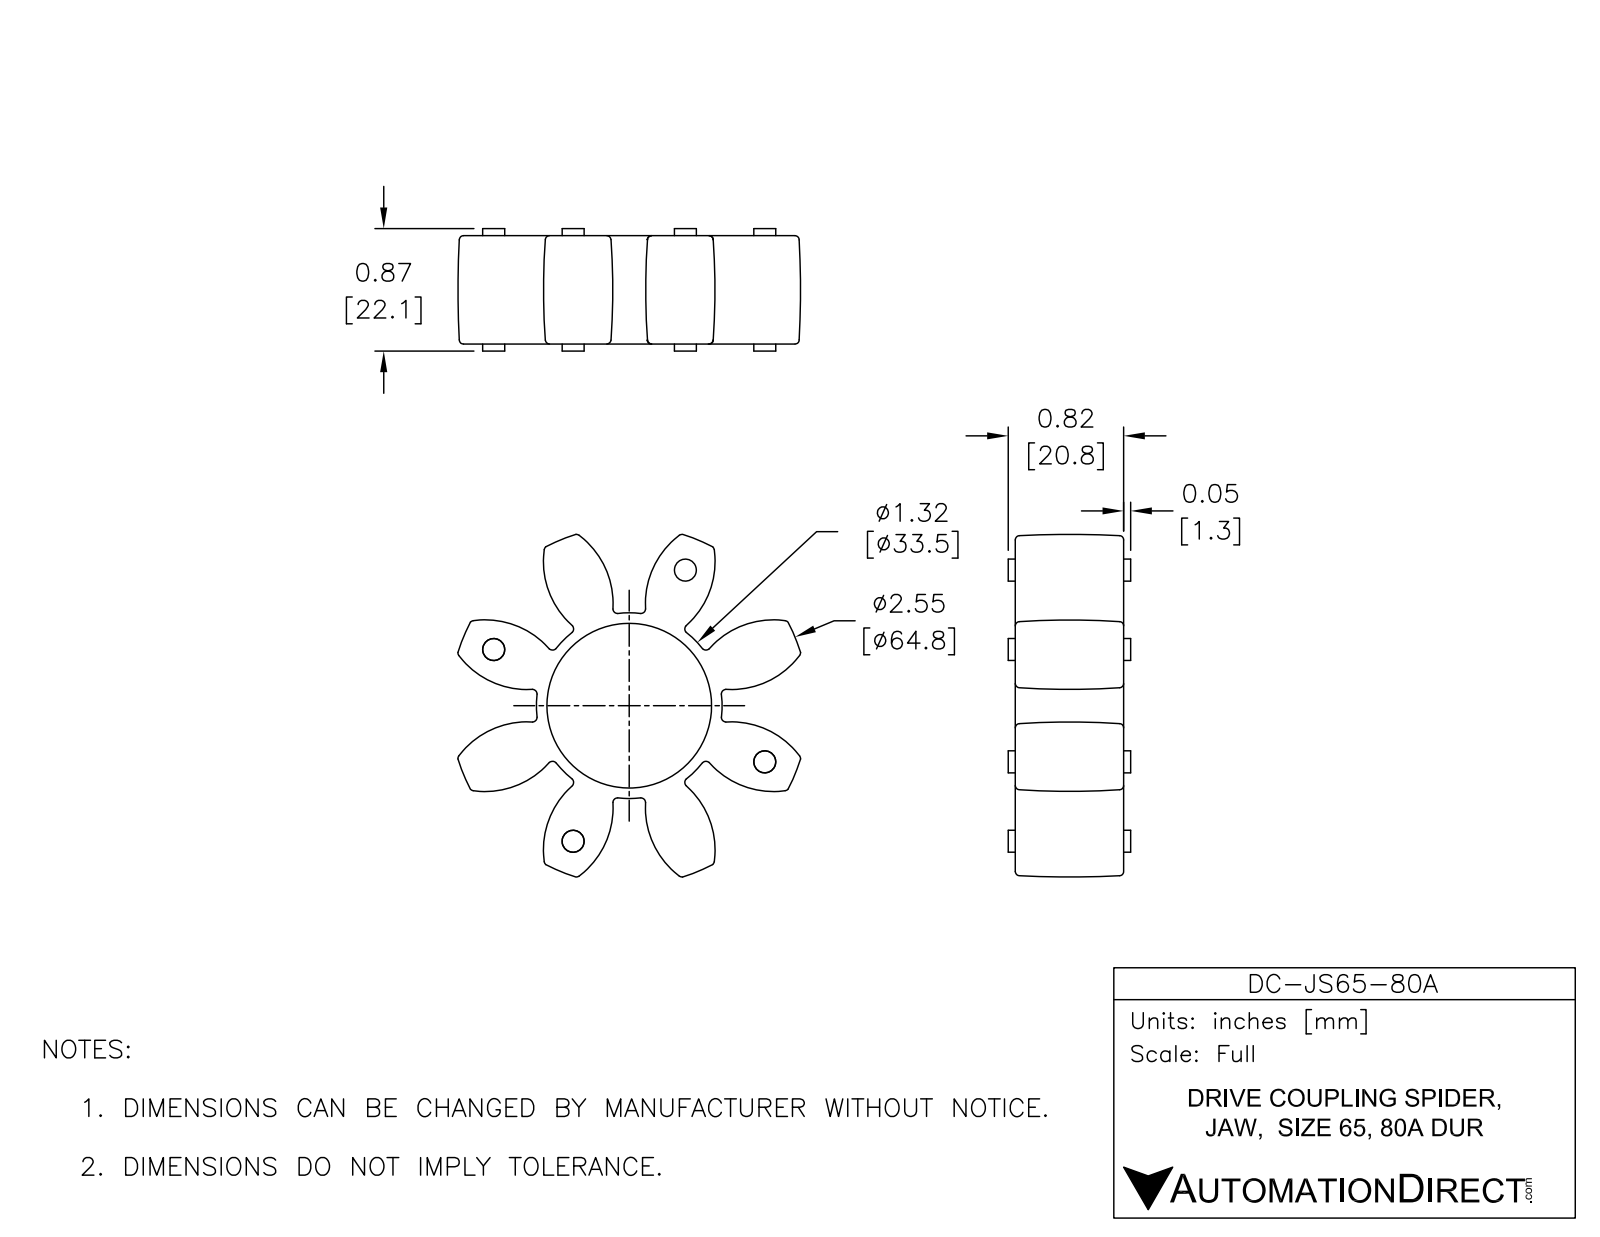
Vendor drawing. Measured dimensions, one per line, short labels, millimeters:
name: DC-JS65-80A
written by: SolidWorks 2015 (AUTOMOTIVE_DESIGN)
unit: mm
bodies: 1 solid, 264 faces (10 planar, 58 cylindrical, 196 other)
size: 61.28 × 61.28 × 22.1
volume: 25 187 mm³; area: 11 168 mm²
holes: 1× ⌀29.72
bosses: 8× ⌀3.96
rounds: 32× R0.75
face distances: 19.56, 1.27, 20.83, 22.1
